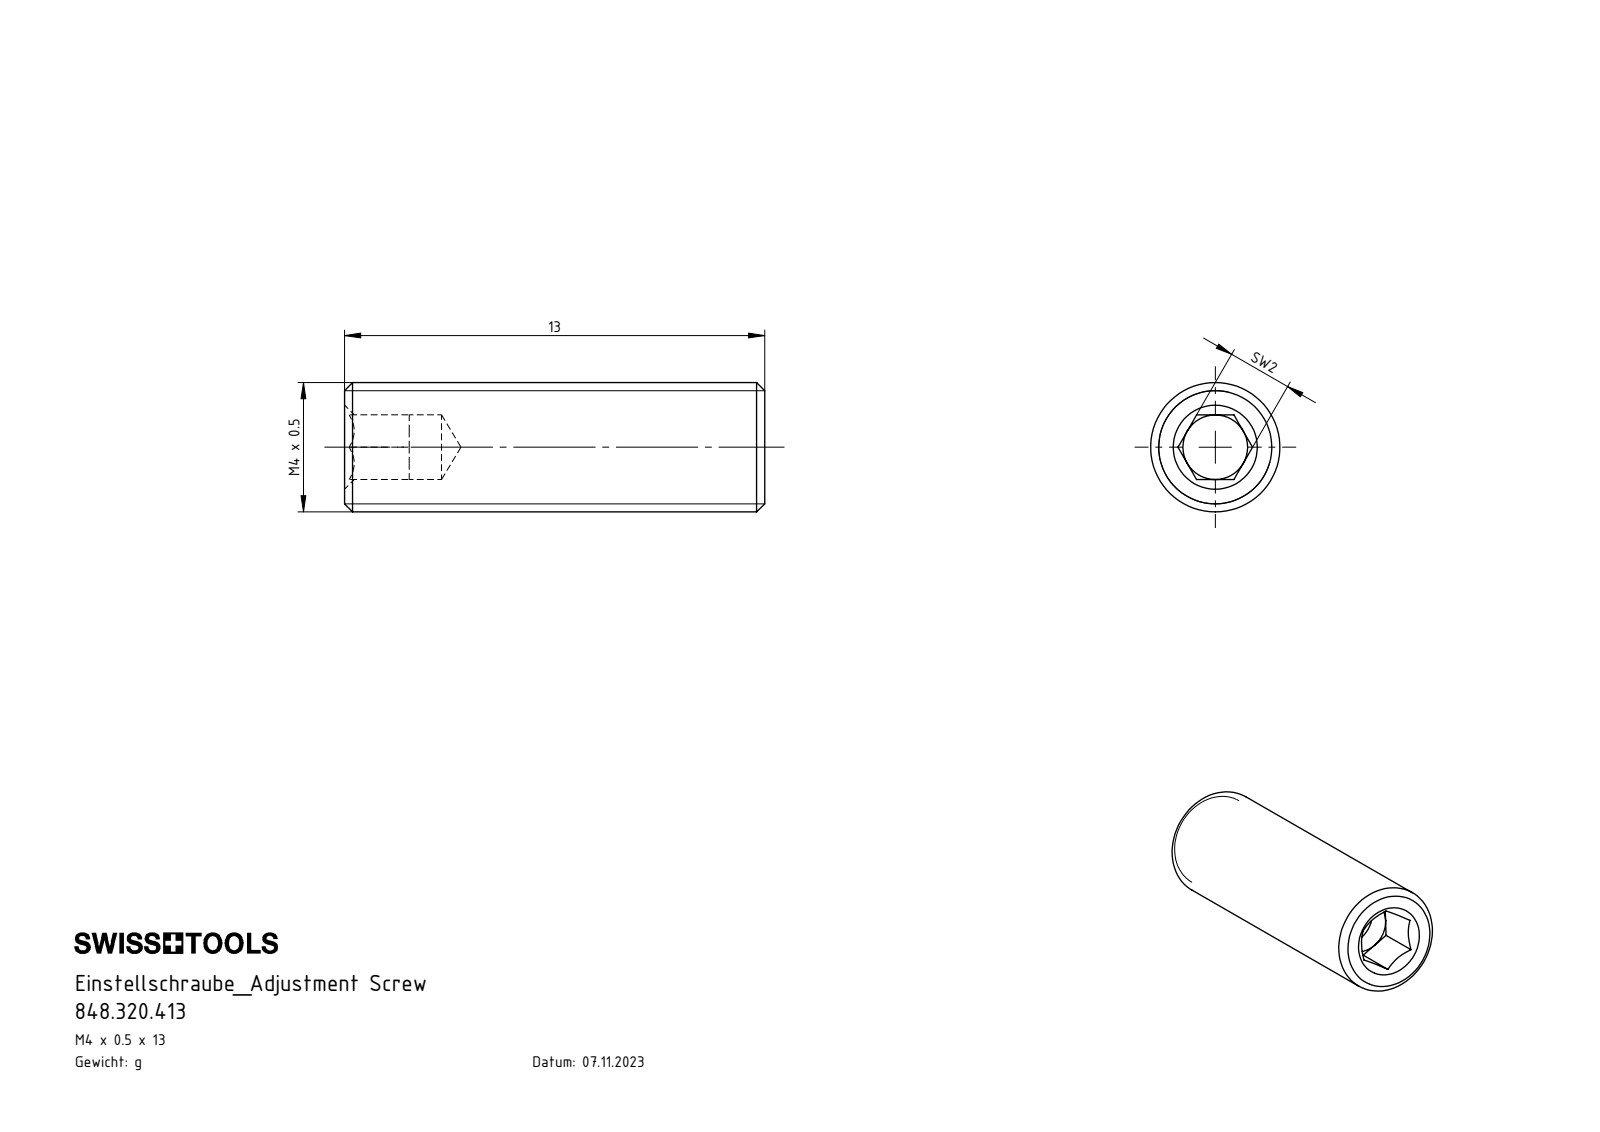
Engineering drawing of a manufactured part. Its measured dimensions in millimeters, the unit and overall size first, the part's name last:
Units: millimetres
Overall size (bounding box): 13 × 4 × 4
Round holes (diameter × count): ⌀2 ×1
Round bosses / shafts (diameter × count): ⌀4 ×1
Main face-to-face distances: 2, 13, 11
Volume: 152 mm³ · Surface area: 204 mm²
Bodies: 1 solid, 26 faces (14 planar, 4 cylindrical, 8 other)
Part name (STEP PRODUCT): 848.320.413
STEP written by: SolidWorks 2022 (AUTOMOTIVE_DESIGN)
